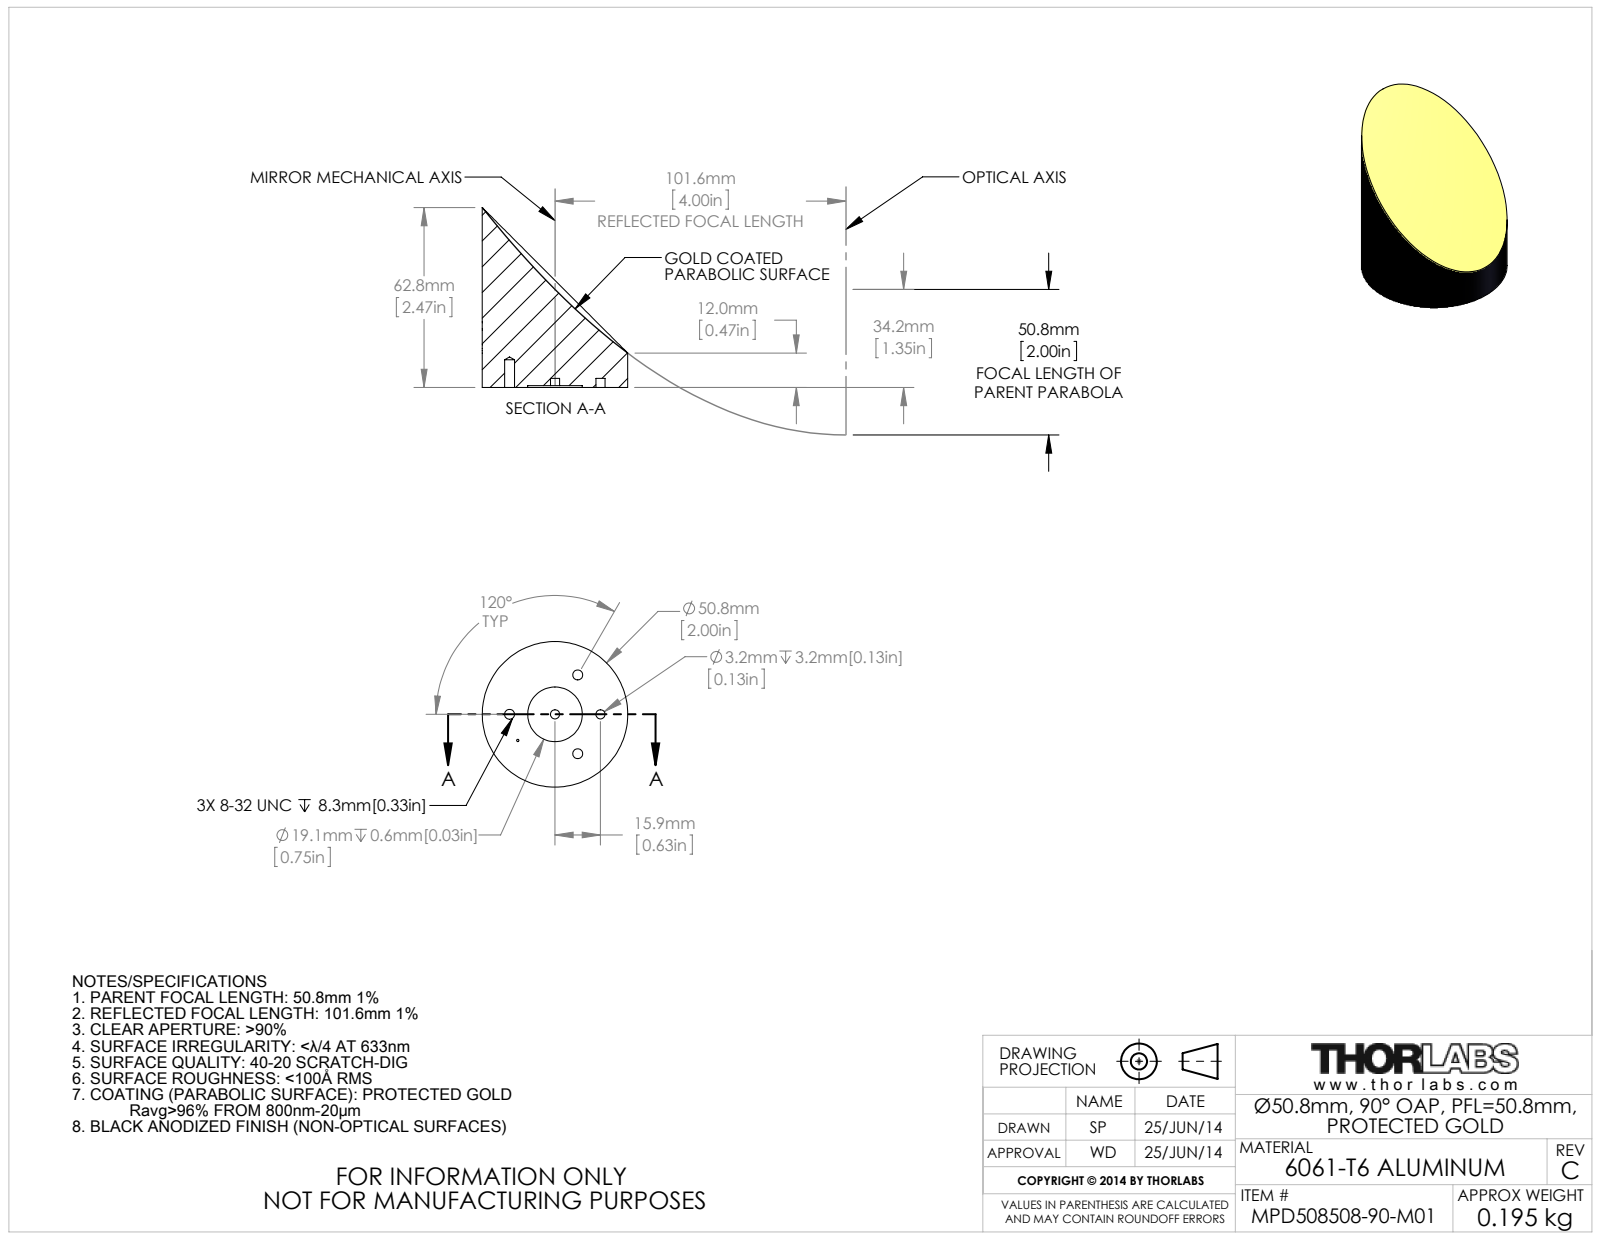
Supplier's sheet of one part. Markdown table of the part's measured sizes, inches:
| quantity | value |
| --- | --- |
| part name | 21176-E0W |
| STEP written by | SolidWorks 2014 (CONFIG_CONTROL_DESIGN) |
| units | inches |
| bodies | 1 solid, 68 faces (4 planar, 54 cylindrical, 10 other) |
| overall size | 2.472 × 2 × 2 |
| volume | 4.399 in³ |
| surface area | 17.51 in² |
| round holes (diameter × count) | 0.136 × 3, 0.126 × 2, 0.75 × 1 |
| round bosses / shafts (diameter × count) | 2 × 1 |
| main face-to-face distances | 0.025, 0.125, 0.1 |
| hole center spacings | 0.625, 0.625, 1.083, 0.624, 1.082, 1.25 |
